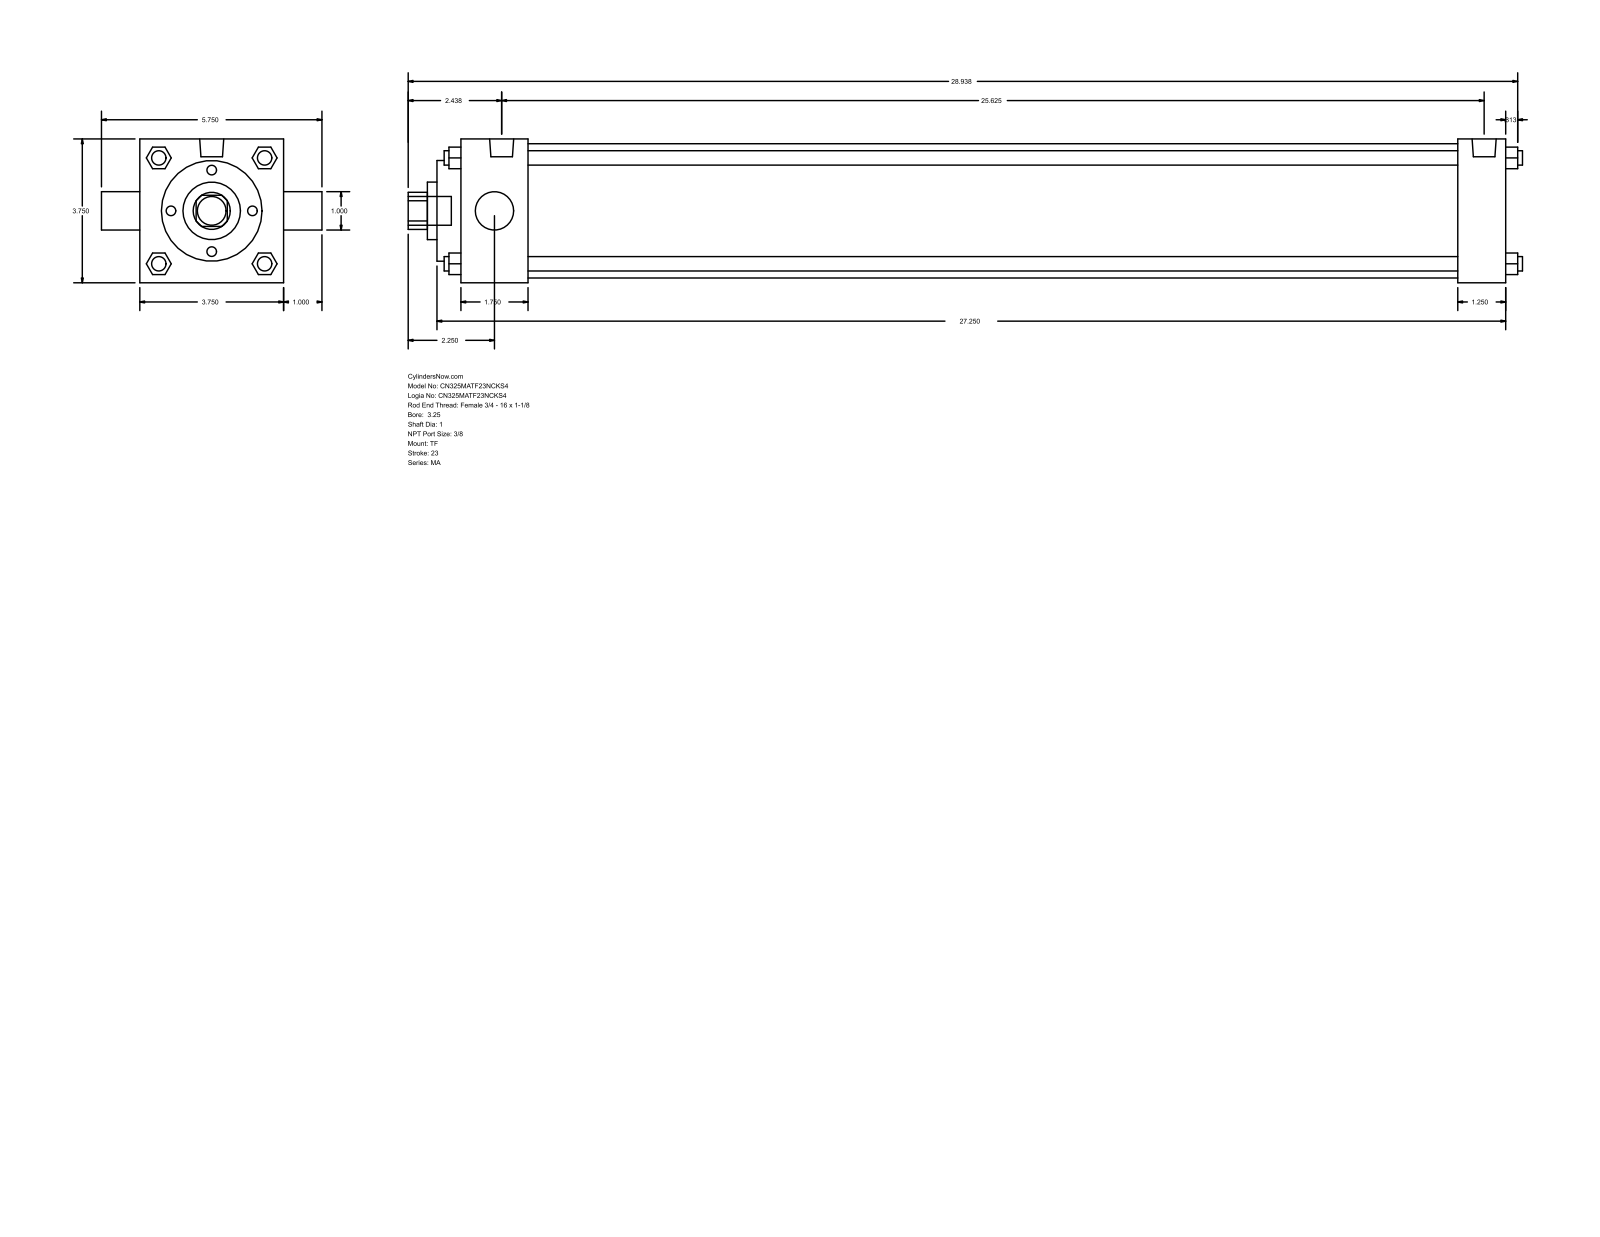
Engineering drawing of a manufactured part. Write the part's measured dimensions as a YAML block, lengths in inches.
part_name: "MA_TF__0325_1"
step_written_by: "GSSL Pune (CONFIG_CONTROL_DESIGN)"
units: inches
bodies: {solids: 0, faces: 122, planar: 93, cylindrical: 29, other: 0}
overall_size: [29.063, 5.75, 3.75]
round_holes:
  - {diameter: 1, count: 2}
  - {diameter: 1.5, count: 1}
  - {diameter: 2.625, count: 1}
  - {diameter: 3.5, count: 1}
round_bosses_or_shafts:
  - {diameter: 0.375, count: 4}
  - {diameter: 0.437, count: 3}
  - {diameter: 0.627, count: 2}
  - {diameter: 0.75, count: 1}
partial_cylinders:
  - {radius: 0.484, count: 1}
face_to_face_distances: [3.75, 27.25, 0.625, 1.75, 26, 24.25, 25.5, 1.25, 2.375, 26.625]
